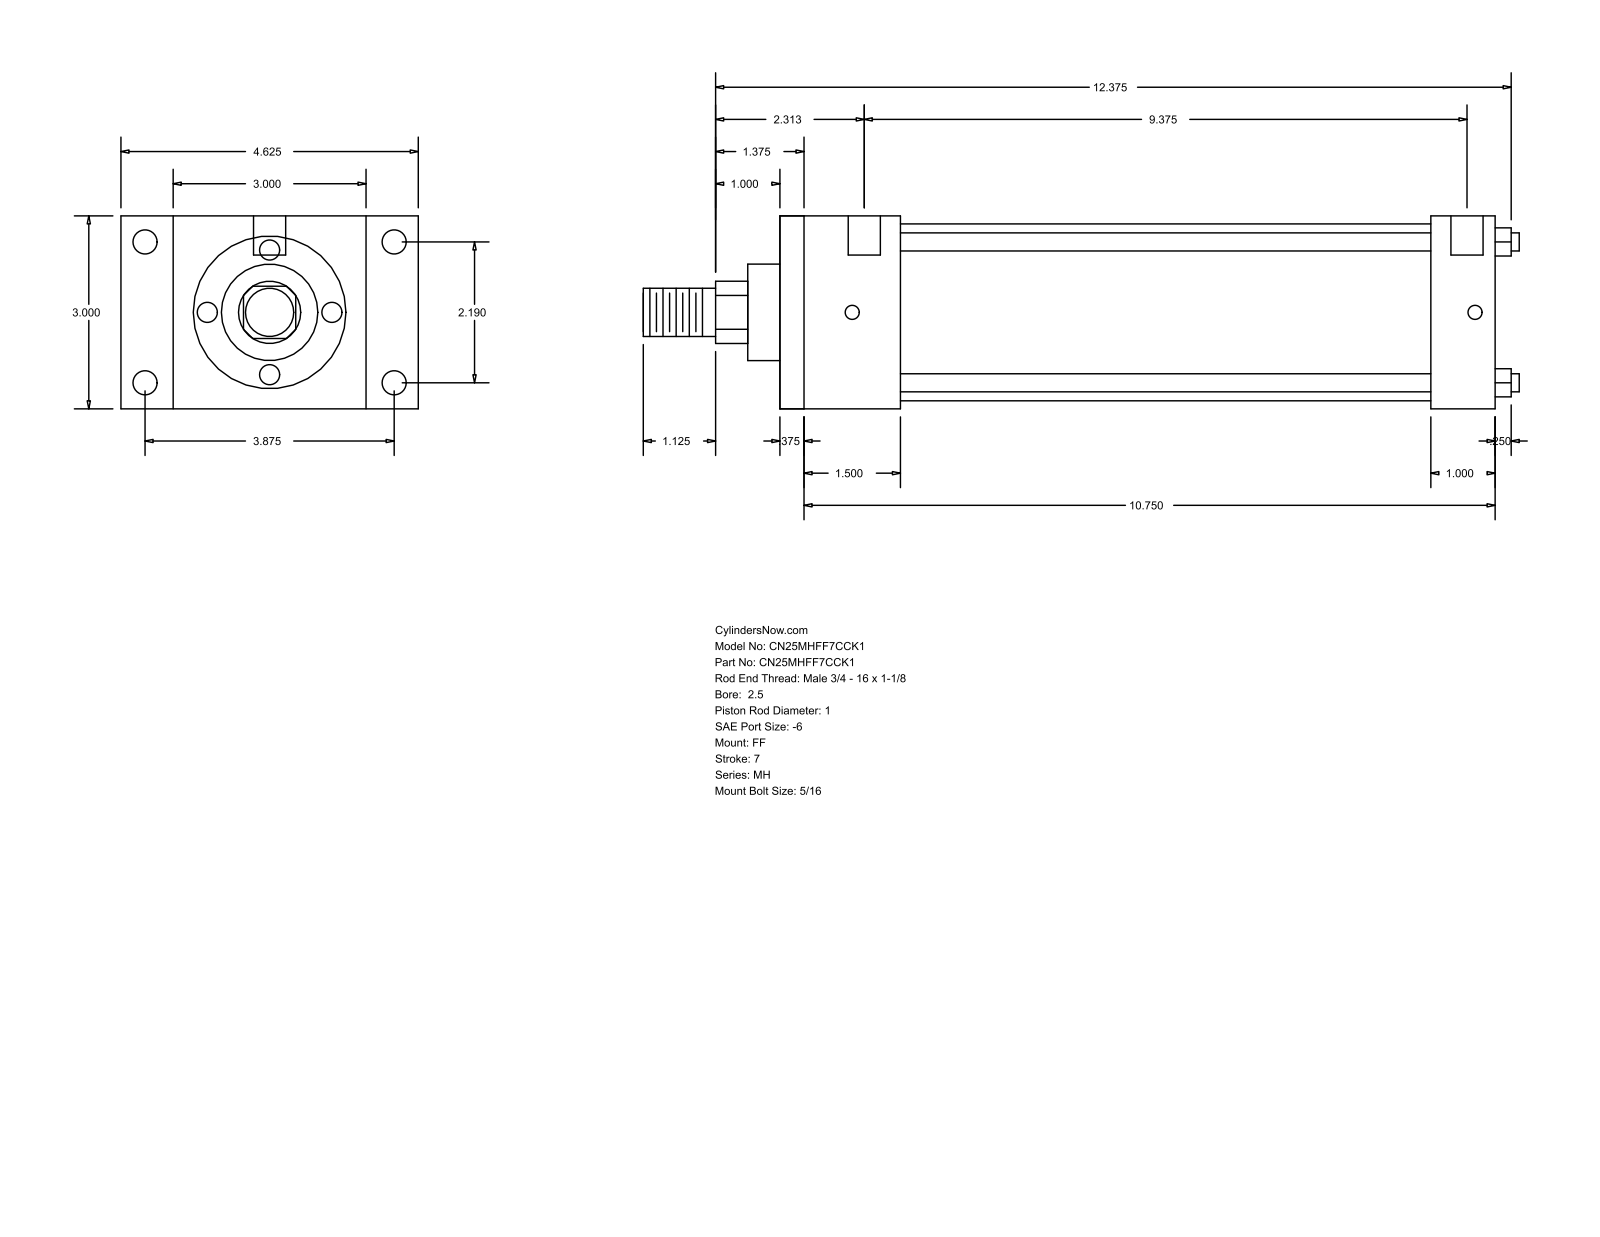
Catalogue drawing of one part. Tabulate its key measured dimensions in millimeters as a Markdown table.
| quantity | value |
| --- | --- |
| part name | MH_FF__0250_1 |
| STEP written by | GSSL Pune (CONFIG_CONTROL_DESIGN) |
| units | millimeters |
| bodies | 0 solids, 92 faces (64 planar, 28 cylindrical, 0 other) |
| overall size | 346.07 × 117.47 × 76.2 |
| round holes (diameter × count) | 5.56 × 4, 9.53 × 4, 12.7 × 2 |
| round bosses / shafts (diameter × count) | 7.14 × 4, 69.85 × 1, 38.1 × 1, 25.4 × 1, 19.05 × 1 |
| partial cylindrical surfaces (radius × count) | 12.29 × 1 |
| main face-to-face distances | 76.2, 282.58, 9.52, 273.06, 47.63, 257.17, 38.11, 247.65, 209.54, 234.95 |
| hole center spacings | 55.62, 98.42, 113.05, 246.06, 3.18, 4.76, 238.12, 241.3 |
